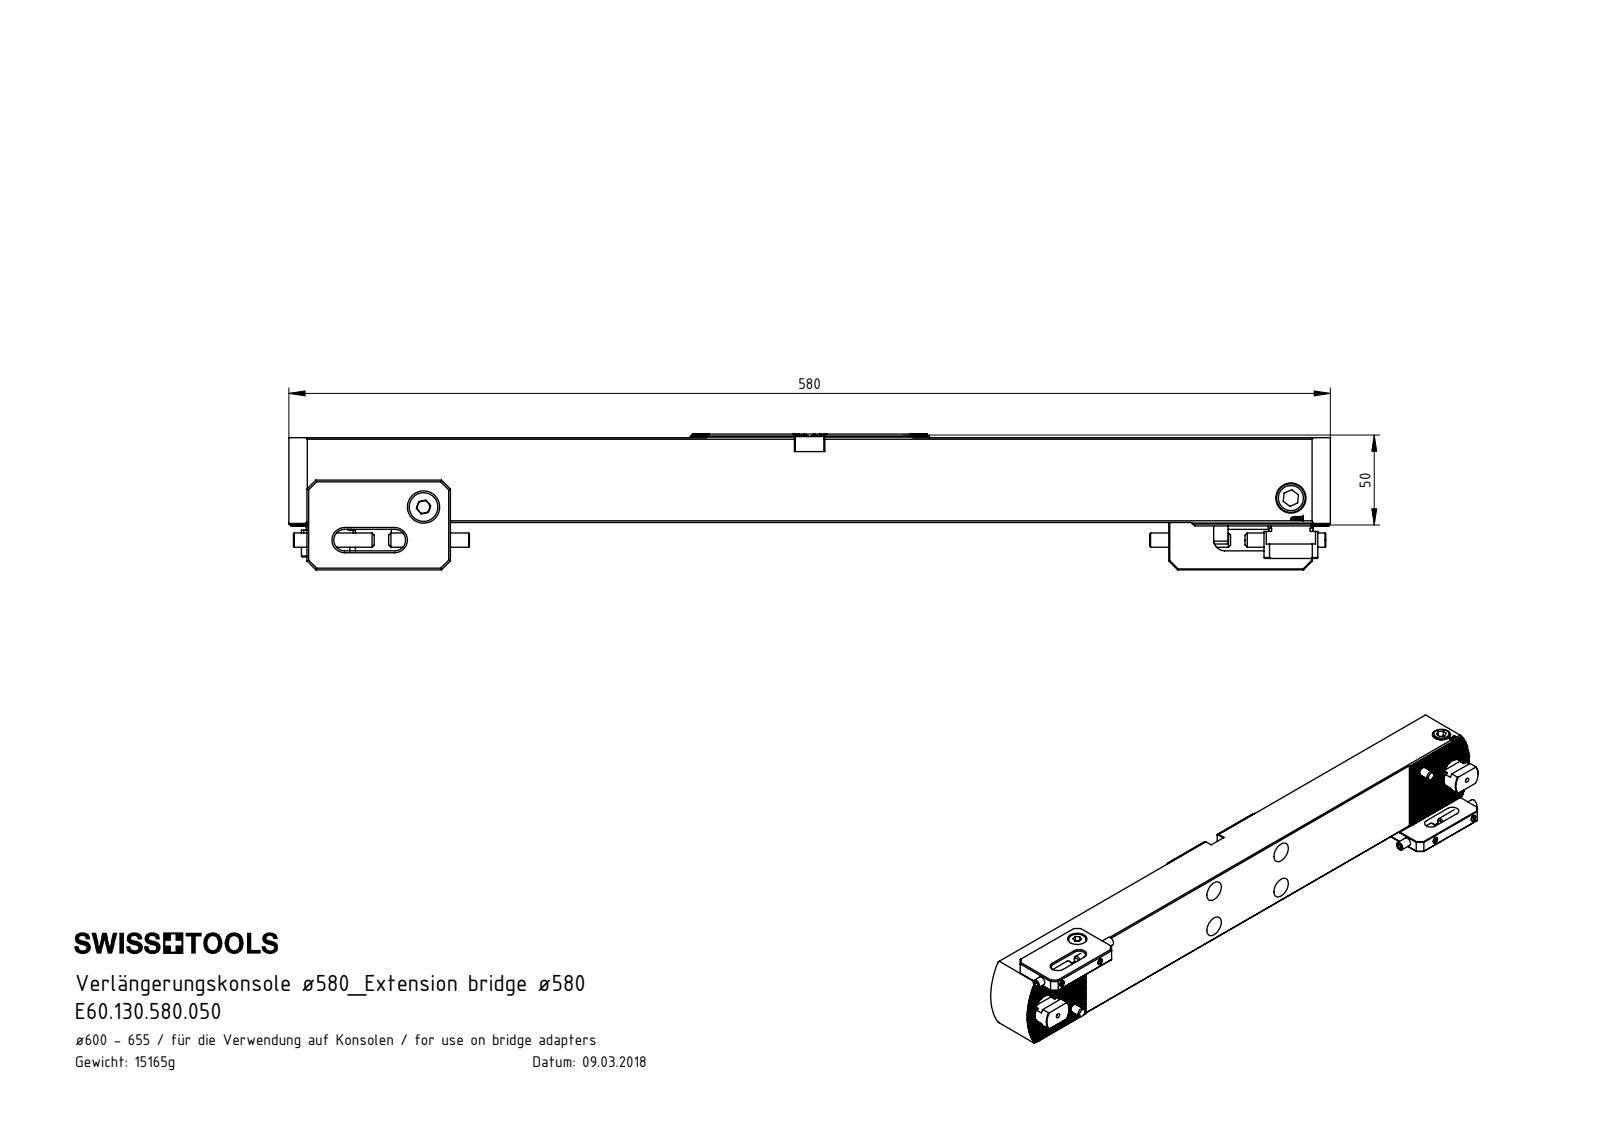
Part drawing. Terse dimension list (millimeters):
name: ISO 8734 - 6 x 12; VK1-ER7.001.012_B; VK1-ER2.201.010_A_vorgespannt; VK1-ER2.201.010_A_gespannt (+8 more)
written by: SolidWorks 2017 (CONFIG_CONTROL_DESIGN)
unit: mm
bodies: 27 solids, 1563 faces (854 planar, 402 cylindrical, 307 other)
size: 580 × 94 × 75.58
volume: 1 938 000 mm³; area: 225 848 mm²
holes: 4× ⌀5, 4× ⌀6, 4× ⌀6.8, 4× ⌀13, 4× ⌀19, 2× ⌀2, 2× ⌀8, 2× ⌀8.5, 2× ⌀10.5, 2× ⌀11, 2× ⌀14, 2× ⌀18
bosses: 4× ⌀16, 4× ⌀6, 2× ⌀10, 2× ⌀8
rounds: 66× R0.14, 8× R2, 4× R6, 2× R12.3, 2× R15, 2× R65, 1× R7.95
face distances: 47.16, 70, 12, 82, 1.73, 8.66, 3.46, 6.93, 0.5, 41.57
hole spacings: 536, 224.89, 312.64, 7.9, 18.55, 19.61, 34.53, 35.09
